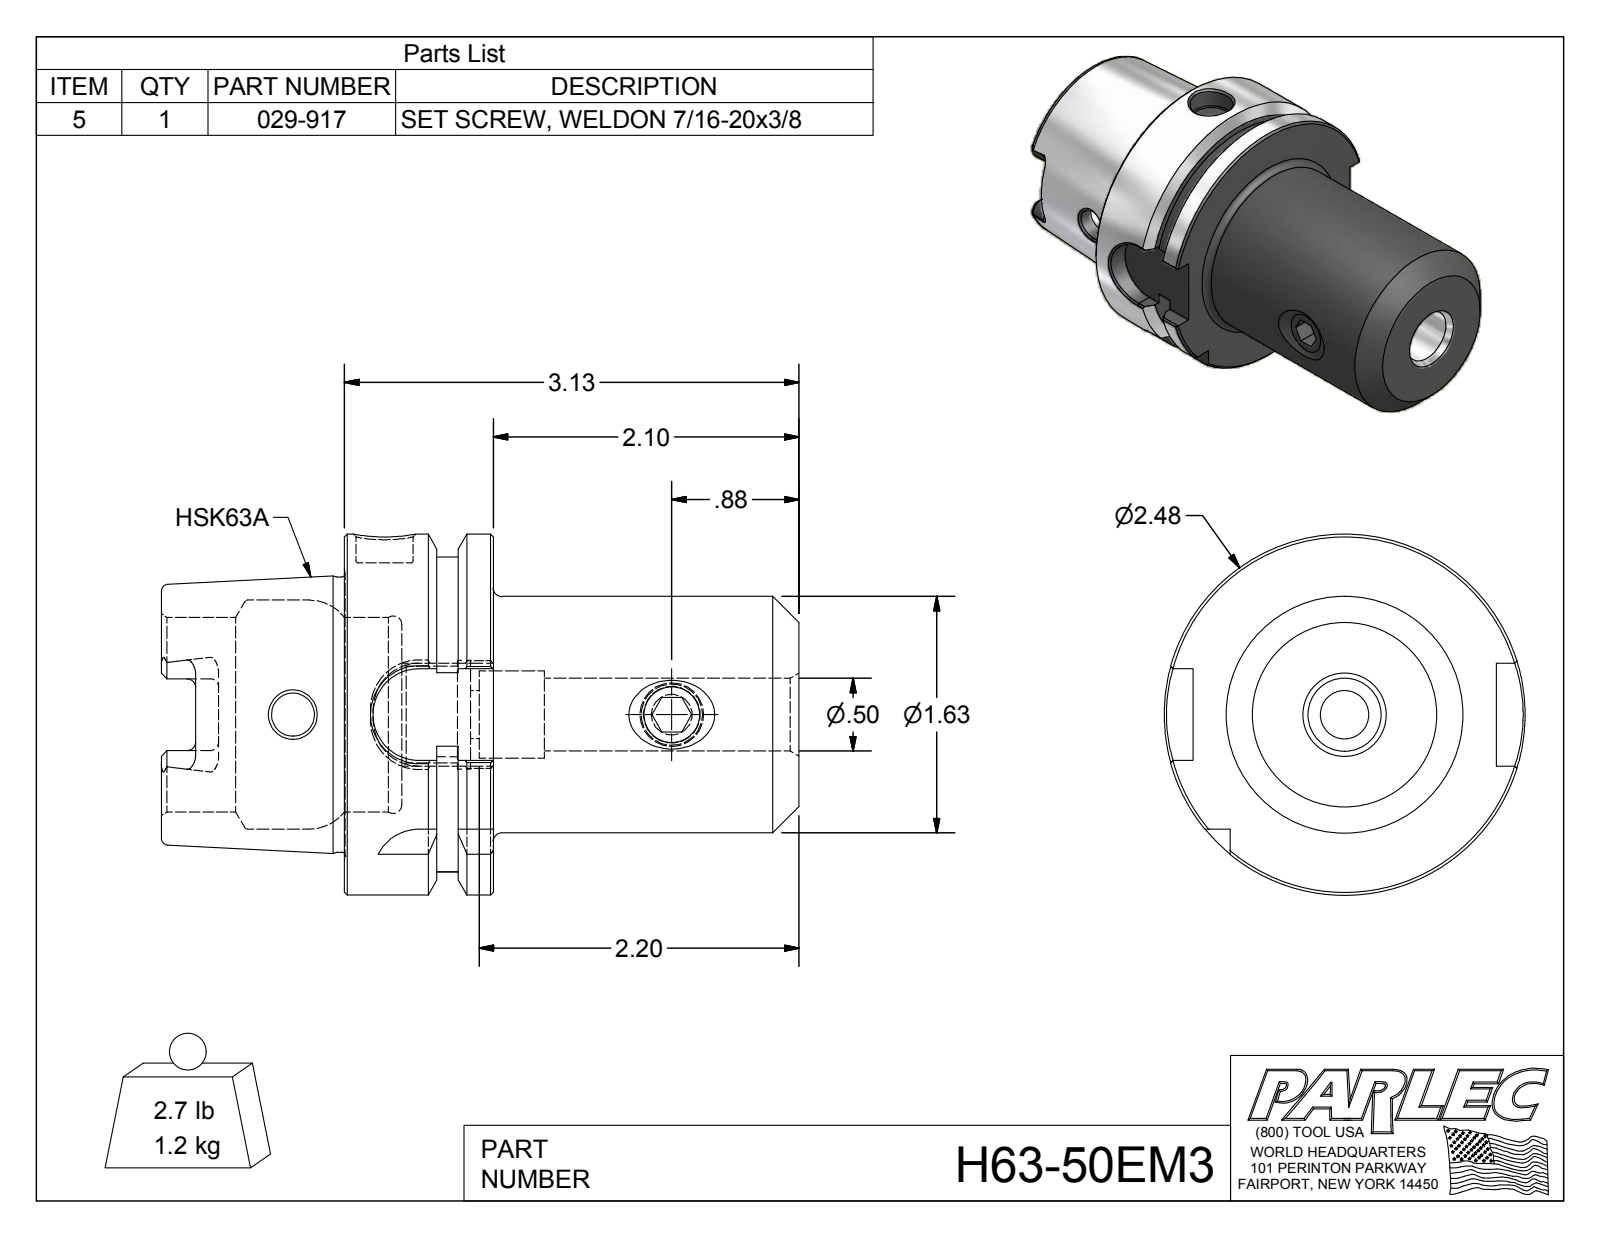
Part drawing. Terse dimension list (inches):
name: H63-50EM3; H63-50EM3-1; 029-917
written by: Autodesk Inventor 2012 (AUTOMOTIVE_DESIGN)
unit: in
bodies: 2 solids, 149 faces (62 planar, 37 cylindrical, 50 other)
size: 4.385 × 2.48 × 2.48
volume: 8.736 in³; area: 49.96 in²
holes: 1× ⌀0.295, 1× ⌀0.331, 1× ⌀0.383, 1× ⌀0.394, 1× ⌀0.5, 1× ⌀0.6, 1× ⌀0.666, 1× ⌀0.749, 1× ⌀1.339, 1× ⌀1.575
bosses: 1× ⌀2.48, 1× ⌀1.891, 1× ⌀1.625, 1× ⌀0.437
rounds: 6× R0.059, 4× R0.113, 4× R0.315, 1× R1.083
face distances: 1.024, 0.241, 0.389, 3.125, 2.102, 0.394, 0.63, 2.731, 1.26, 1.654
hole spacings: 2.604
